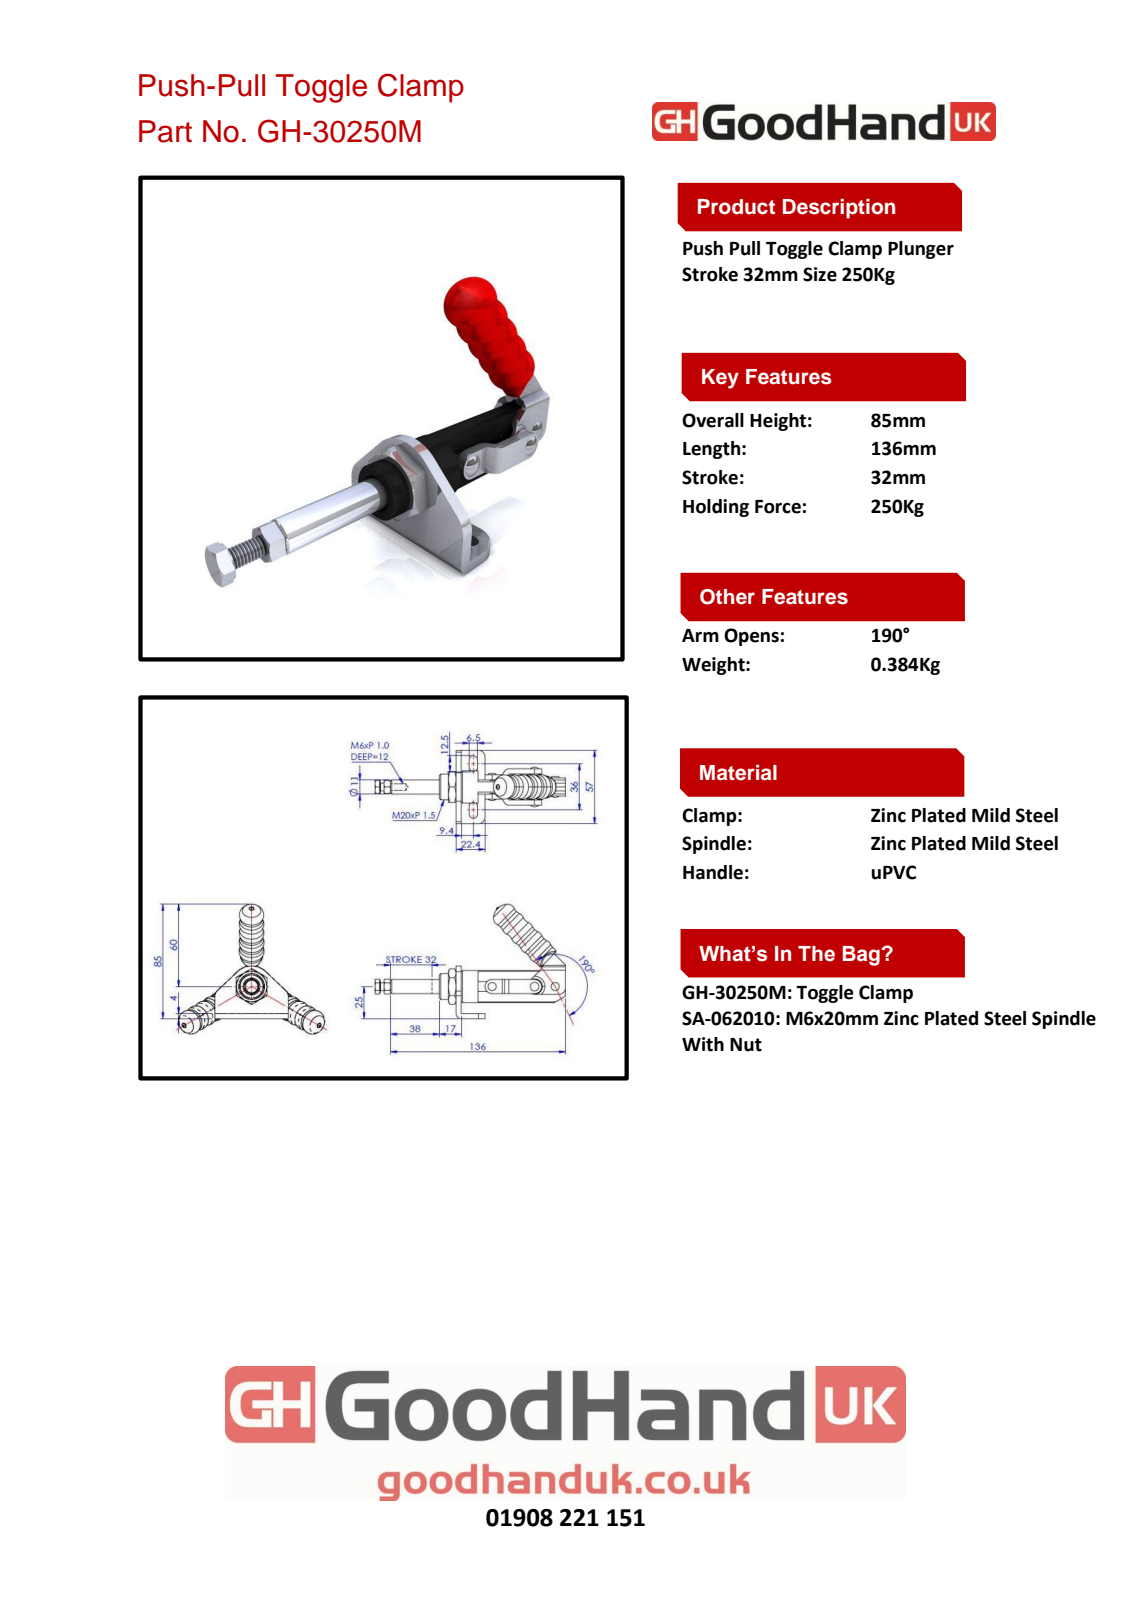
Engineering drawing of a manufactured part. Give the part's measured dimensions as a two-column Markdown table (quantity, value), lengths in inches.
| quantity | value |
| --- | --- |
| part name | 4303233-1^GH-30250M(簡化); Group6^GH-30250M(簡化); Group3^GH-30250M(簡化); Group2^GH-30250M(簡化) (+3 more) |
| STEP written by | SolidWorks 2016 (AUTOMOTIVE_DESIGN) |
| units | inches |
| bodies | 5 solids, 351 faces (141 planar, 92 cylindrical, 118 other) |
| overall size | 5.827 × 3.346 × 2.244 |
| volume | 3.53 in³ |
| surface area | 47.39 in² |
| round holes (diameter × count) | 0.138 × 3, 0.197 × 1, 0.236 × 1, 0.433 × 1, 0.728 × 1, 0.795 × 1 |
| round bosses / shafts (diameter × count) | 0.23 × 2, 0.984 × 1, 0.787 × 1, 0.434 × 1, 0.394 × 1, 0.228 × 1 |
| partial cylindrical surfaces (radius × count) | 0.158 × 5, 0.197 × 5, 0.119 × 4, 0.128 × 4, 0.236 × 3, 0.217 × 2, 0.244 × 1, 0.63 × 1 |
| main face-to-face distances | 0.157, 0.118, 0.315, 0.276, 0.236, 0.559, 0.394, 0.437, 0.24, 0.555 |
| hole center spacings | 0.63, 1.299, 1.929 |
